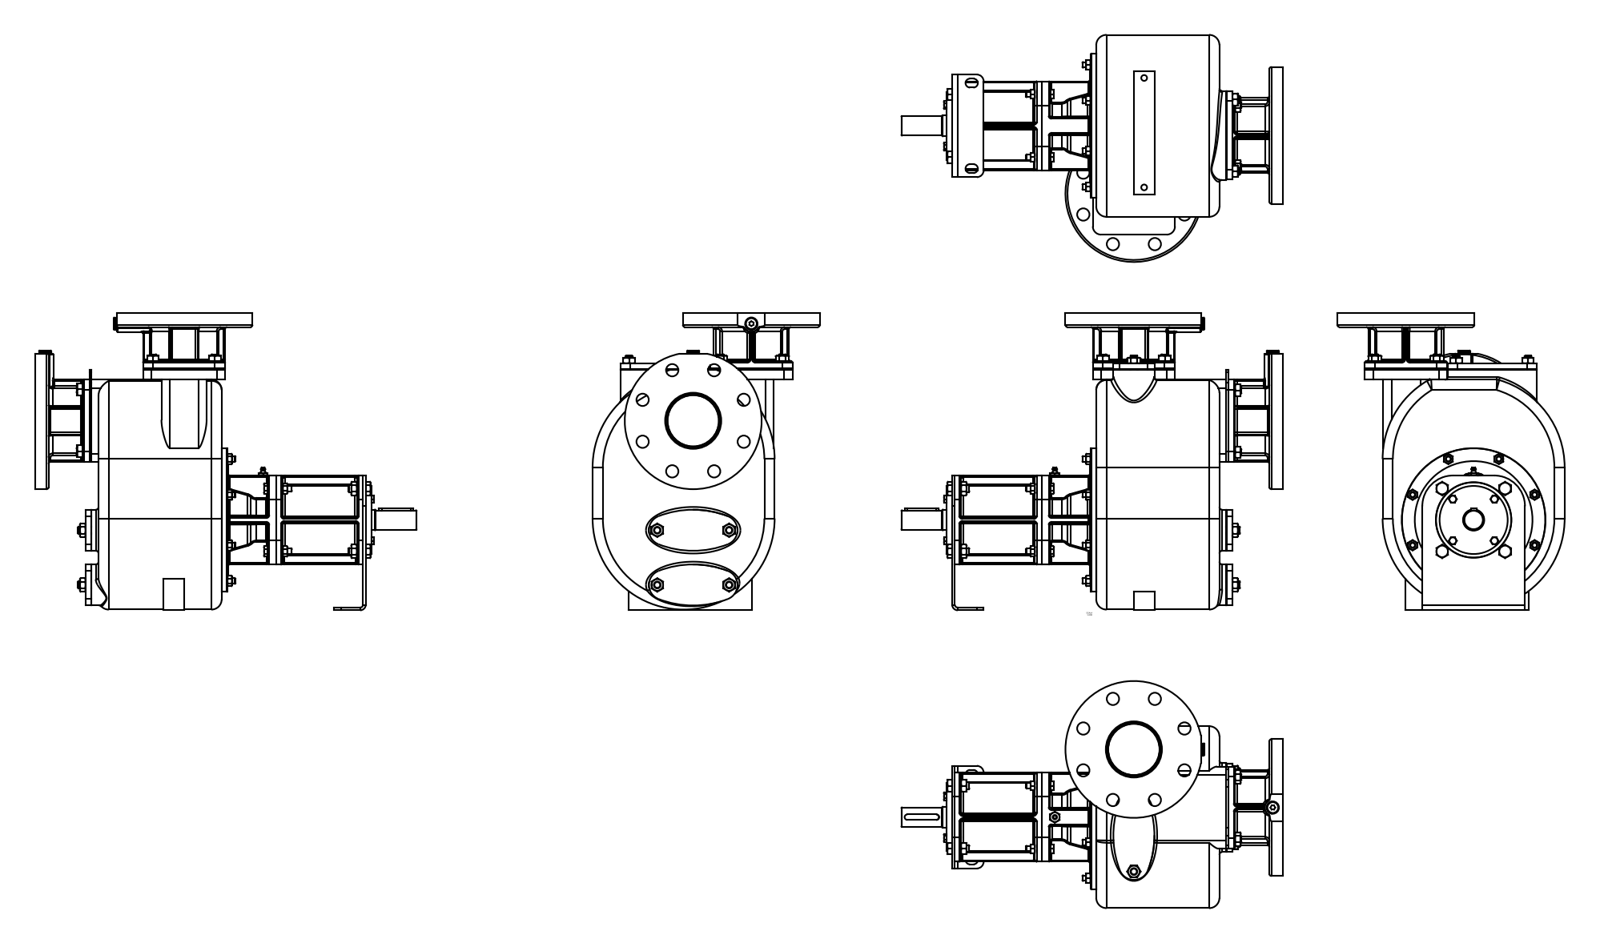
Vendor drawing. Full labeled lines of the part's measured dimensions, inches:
Part name (STEP PRODUCT): S_83_B_F
STEP written by: CREO PARAMETRIC BY PTC INC, 2017110 (CONFIG_CONTROL_DESIGN)
Units: inches
Bodies: 2 solids, 920 faces (188 planar, 420 cylindrical, 312 other)
Overall size (bounding box): 21.949 × 17.087 × 13.071
Volume: 1 124 in³ · Surface area: 1 282 in²
Round holes (diameter × count): ⌀0.709 ×16, ⌀0.453 ×14, ⌀0.394 ×12, ⌀0.433 ×12, ⌀0.276 ×4, ⌀0.335 ×2, ⌀0.463 ×2, ⌀2.953 ×2, ⌀3.15 ×2, ⌀1.22 ×1, ⌀2.48 ×1, ⌀3.543 ×1
Round bosses / shafts (diameter × count): ⌀7.874 ×2, ⌀8.268 ×1, ⌀6.772 ×1, ⌀3.937 ×1, ⌀3.917 ×1, ⌀1.181 ×1, ⌀1.102 ×1
Partial cylindrical surfaces — rounded edges, fillets, slot ends (radius × count): R0.118 ×76, R0.079 ×70, R0.591 ×15, R0.472 ×14, R5.512 ×6, R0.157 ×4, R0.256 ×4, R0.866 ×4
Main face-to-face distances: 0.354, 7.087, 0.787, 0.039, 7.854, 3.661, 7.756, 10.748, 0.315, 2.874
Hole centre spacings: 1.267, 3.15, 3.193, 4.454, 4.727, 5.561, 6.299, 2.41
